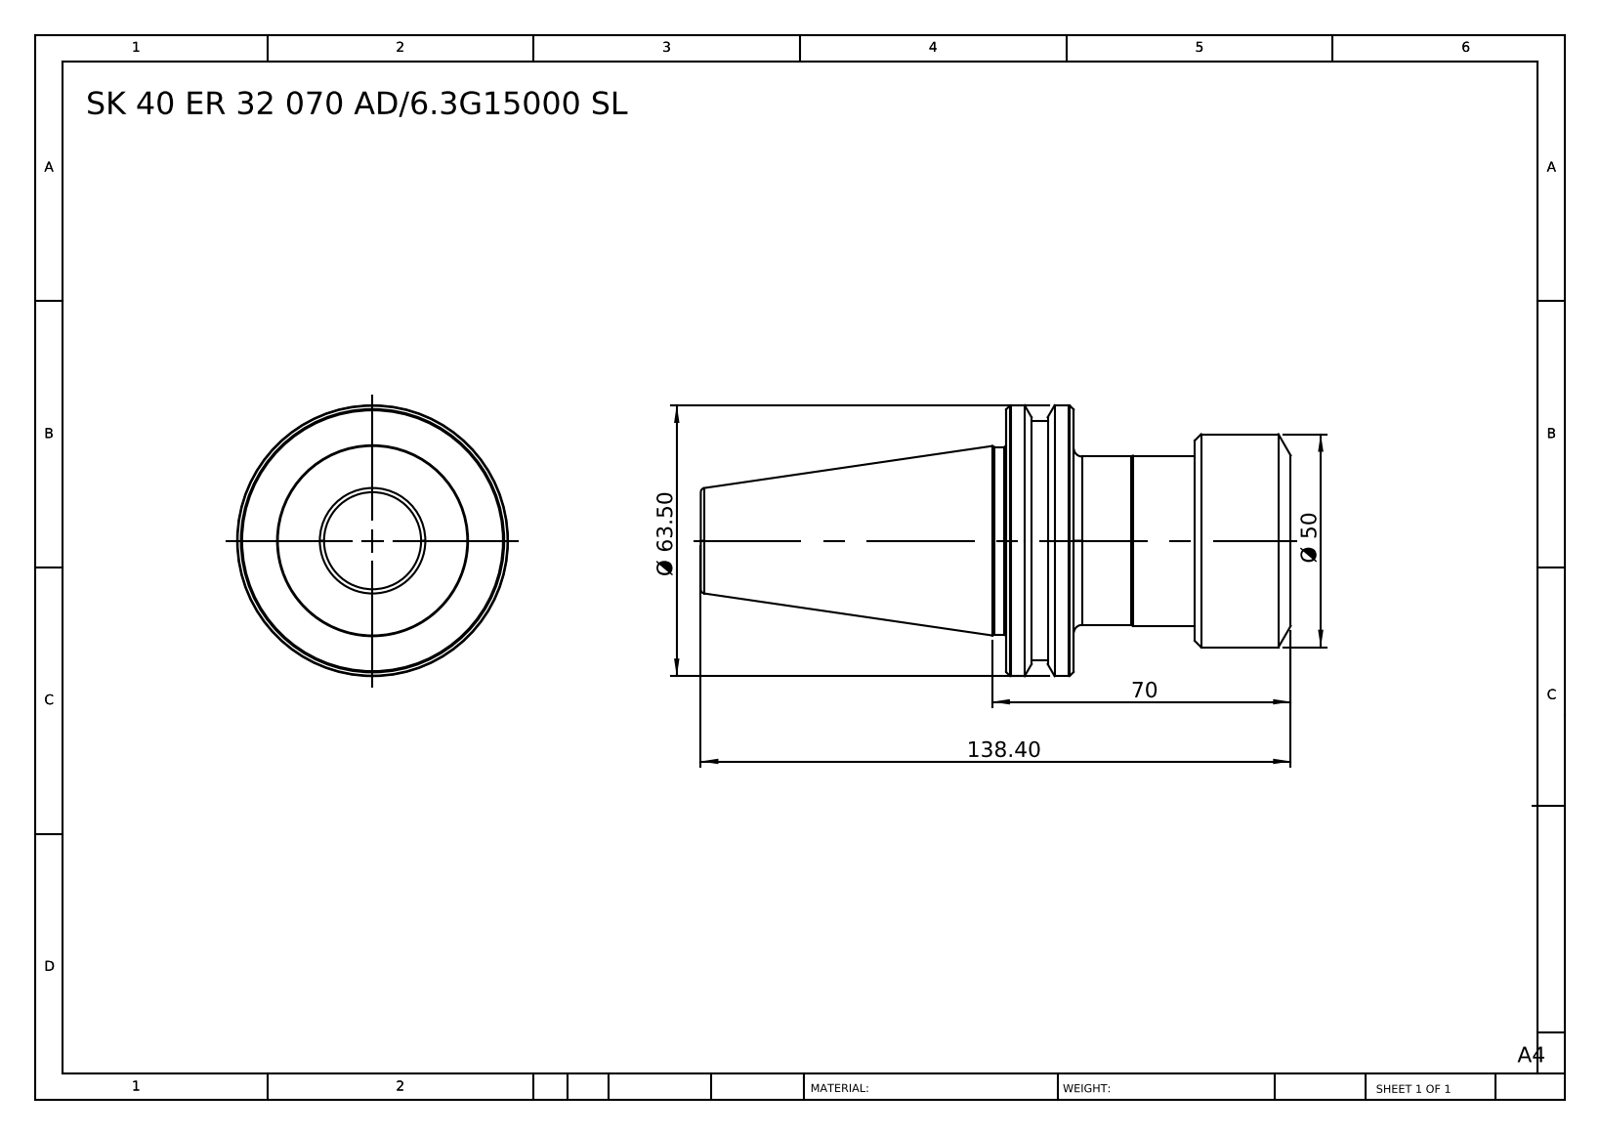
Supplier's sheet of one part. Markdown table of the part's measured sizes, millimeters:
| quantity | value |
| --- | --- |
| part name | SK 40 ER 32 070 AD-6.3G15000 SL |
| STEP written by | SolidWorks 2014 (CONFIG_CONTROL_DESIGN) |
| units | millimeters |
| bodies | 1 solid, 53 faces (7 planar, 14 cylindrical, 32 other) |
| overall size | 138.4 × 63.54 × 63.54 |
| volume | 195 425 mm³ |
| surface area | 24 882 mm² |
| round bosses / shafts (diameter × count) | 63.54 × 1, 56.04 × 1, 50 × 1, 44 × 1, 39.9 × 1, 39.5 × 1 |
| main face-to-face distances | 15.92, 50.89, 66.81, 22.5, 28.39, 44.31, 138.4, 115.9, 87.51, 71.59 |
